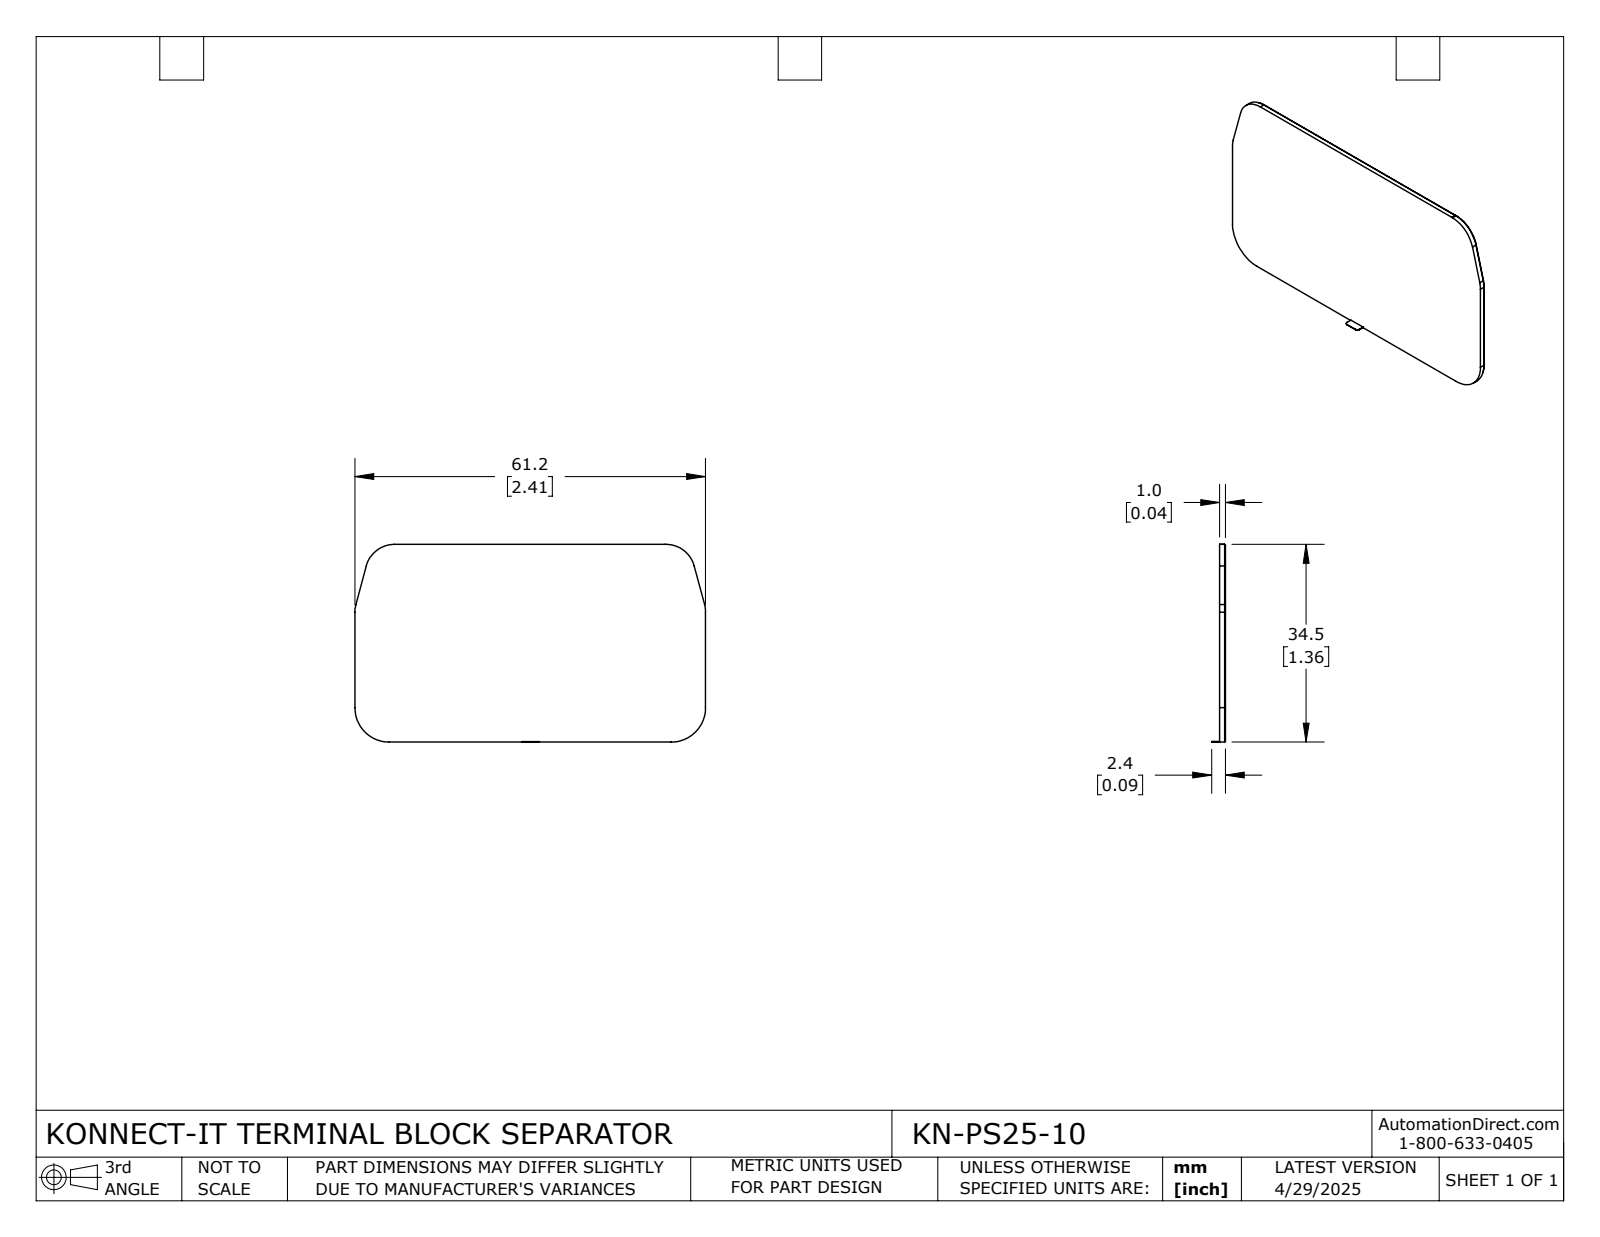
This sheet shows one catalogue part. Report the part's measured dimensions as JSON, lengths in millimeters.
{"part_name": "KN-PS25-10", "step_written_by": "SolidWorks 2024 (CONFIG_CONTROL_DESIGN)", "units": "millimeters", "bodies": {"solids": 1, "faces": 35, "planar": 21, "cylindrical": 14, "other": 0}, "overall_size": [61.23, 34.51, 2.4], "volume_mm3": 2056, "surface_area_mm2": 4304, "partial_cylinders_radius": [[5, 4], [5.1, 4], [0.5, 2], [5.9, 2], [6, 2]], "face_to_face_distances": [1, 34.51, 34.41, 0.85, 61.23, 34.31, 61.13, 61.03, 1.4, 2.25]}
